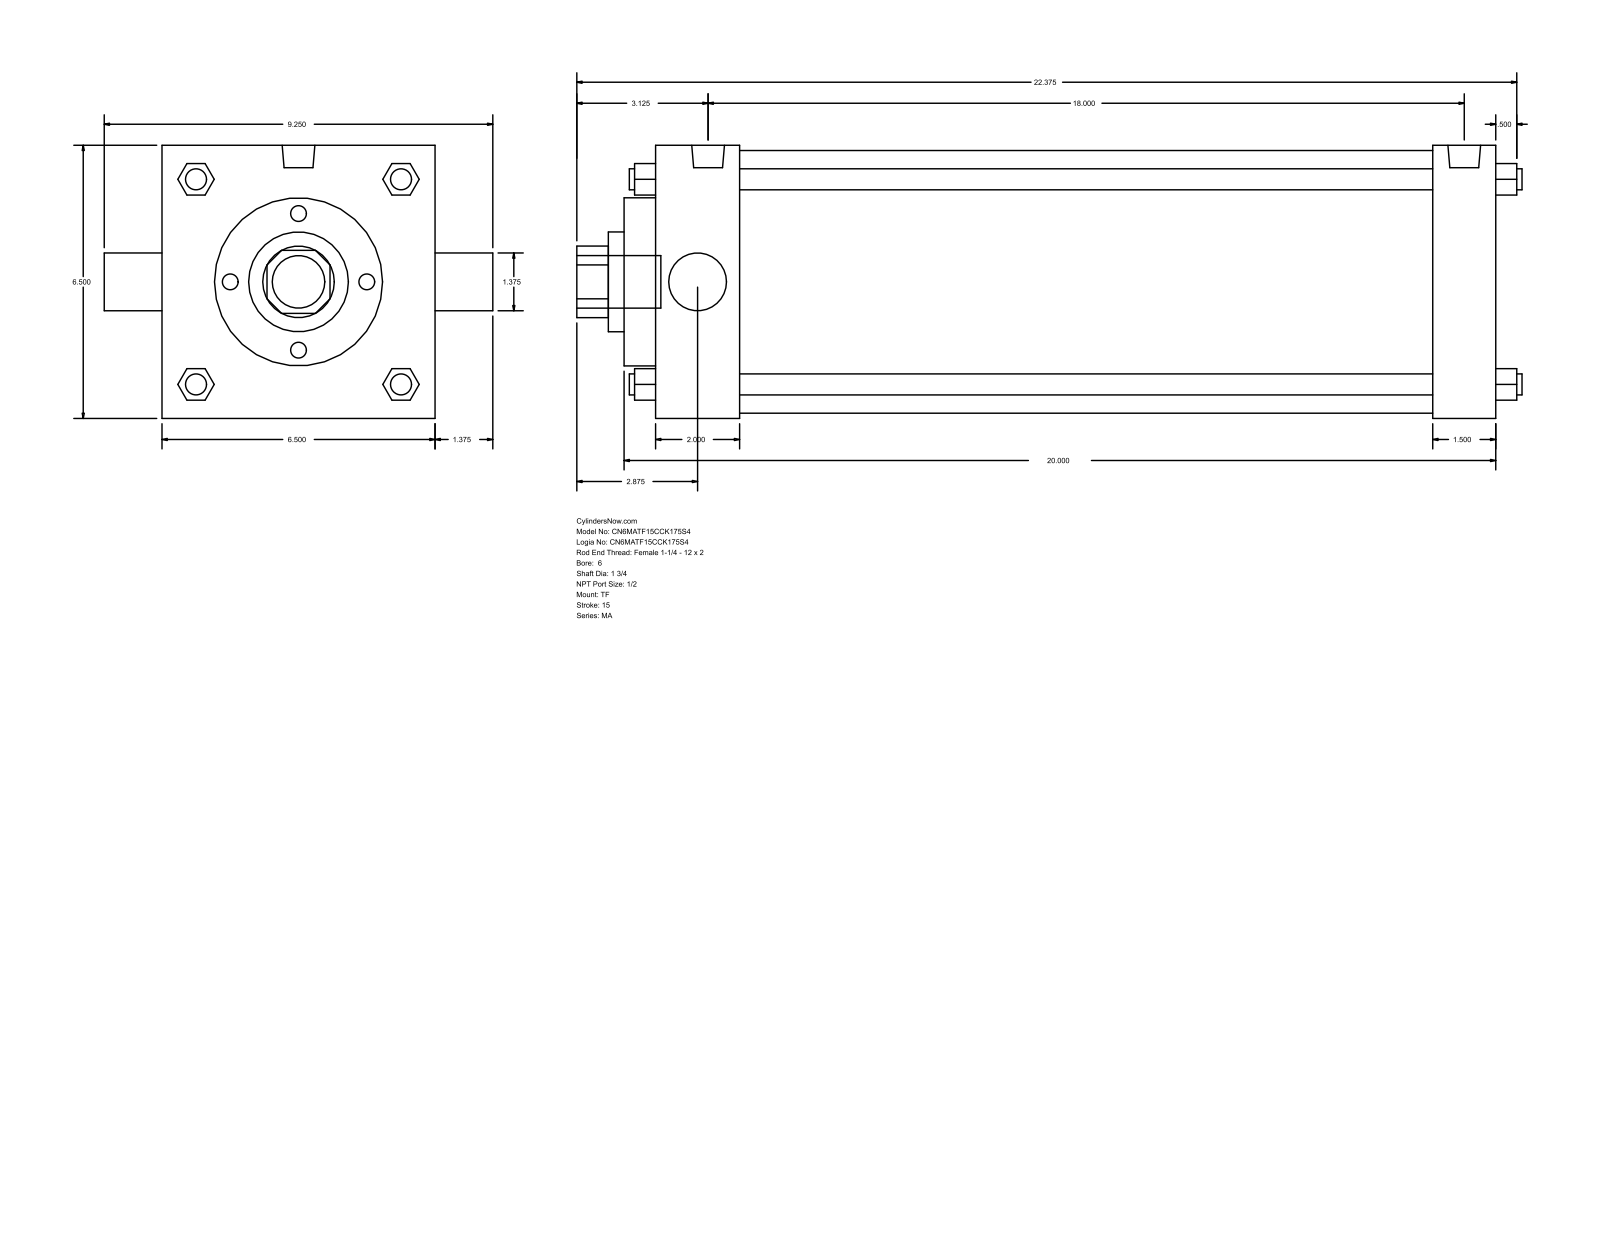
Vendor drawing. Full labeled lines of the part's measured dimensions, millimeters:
Part name (STEP PRODUCT): MA_TF__0600_1.75
STEP written by: GSSL Pune (CONFIG_CONTROL_DESIGN)
Units: millimetres
Bodies: 0 solids, 122 faces (93 planar, 29 cylindrical, 0 other)
Overall size (bounding box): 571.5 × 234.95 × 165.1
Round holes (diameter × count): ⌀34.92 ×1, ⌀44.45 ×1, ⌀60.33 ×1, ⌀101.6 ×1, ⌀158.75 ×1
Round bosses / shafts (diameter × count): ⌀12.7 ×4, ⌀17.46 ×3, ⌀19.77 ×2, ⌀31.75 ×1
Partial cylindrical surfaces — rounded edges, fillets, slot ends (radius × count): R21.63 ×1
Main face-to-face distances: 165.1, 508, 19.05, 38.1, 50.8, 457.2, 469.9, 419.1, 69.85, 488.95
